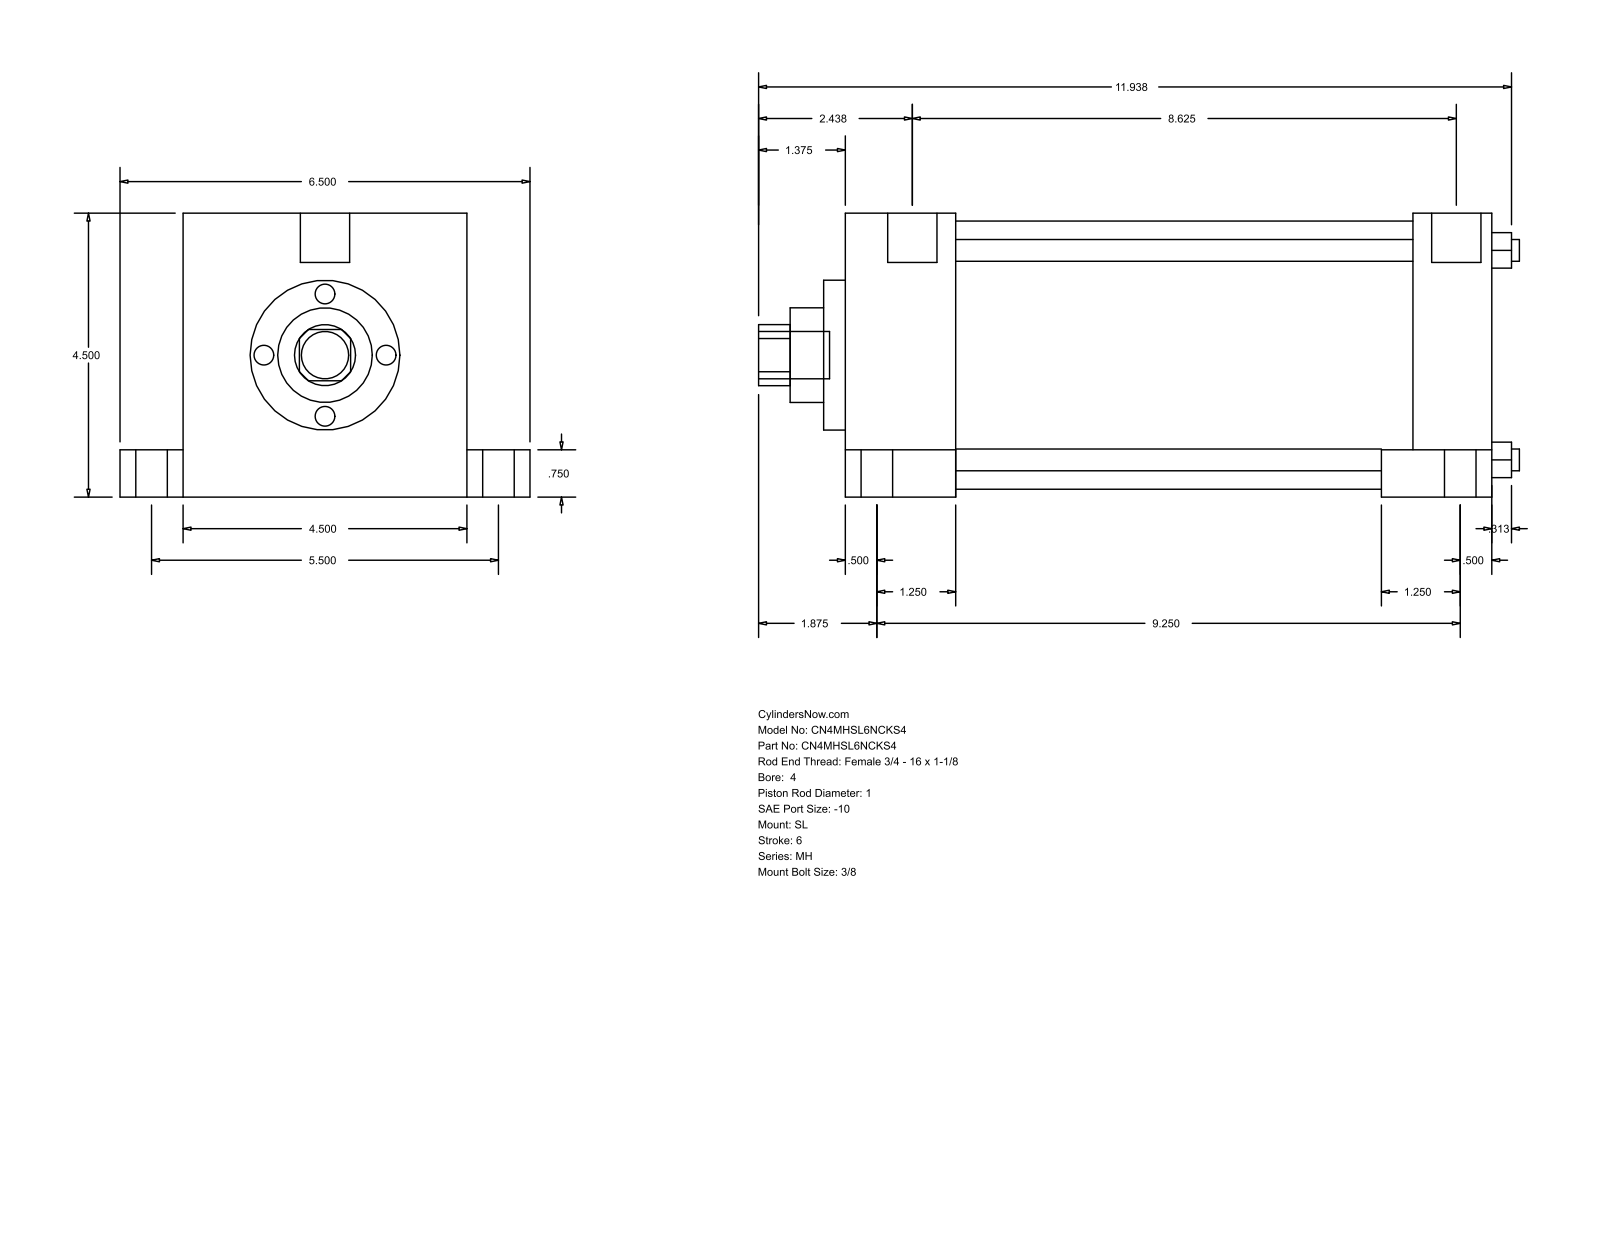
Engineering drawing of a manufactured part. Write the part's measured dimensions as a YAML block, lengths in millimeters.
part_name: "MH_SL__0400_1"
step_written_by: "GSSL Pune (CONFIG_CONTROL_DESIGN)"
units: millimeters
bodies: {solids: 0, faces: 110, planar: 77, cylindrical: 33, other: 0}
overall_size: [306.39, 165.1, 114.3]
round_holes:
  - {diameter: 8.76, count: 4}
  - {diameter: 25.4, count: 1}
  - {diameter: 38.1, count: 1}
  - {diameter: 60.33, count: 1}
  - {diameter: 107.95, count: 1}
round_bosses_or_shafts:
  - {diameter: 19.05, count: 5}
  - {diameter: 12.7, count: 4}
  - {diameter: 8.73, count: 4}
  - {diameter: 19.84, count: 2}
partial_cylinders:
  - {radius: 12.29, count: 1}
face_to_face_distances: [114.3, 260.35, 44.46, 215.89, 228.6, 184.14, 31.75, 25.4, 139.7, 19.05]
hole_center_spacings: [59.62, 84.32, 119.25]
